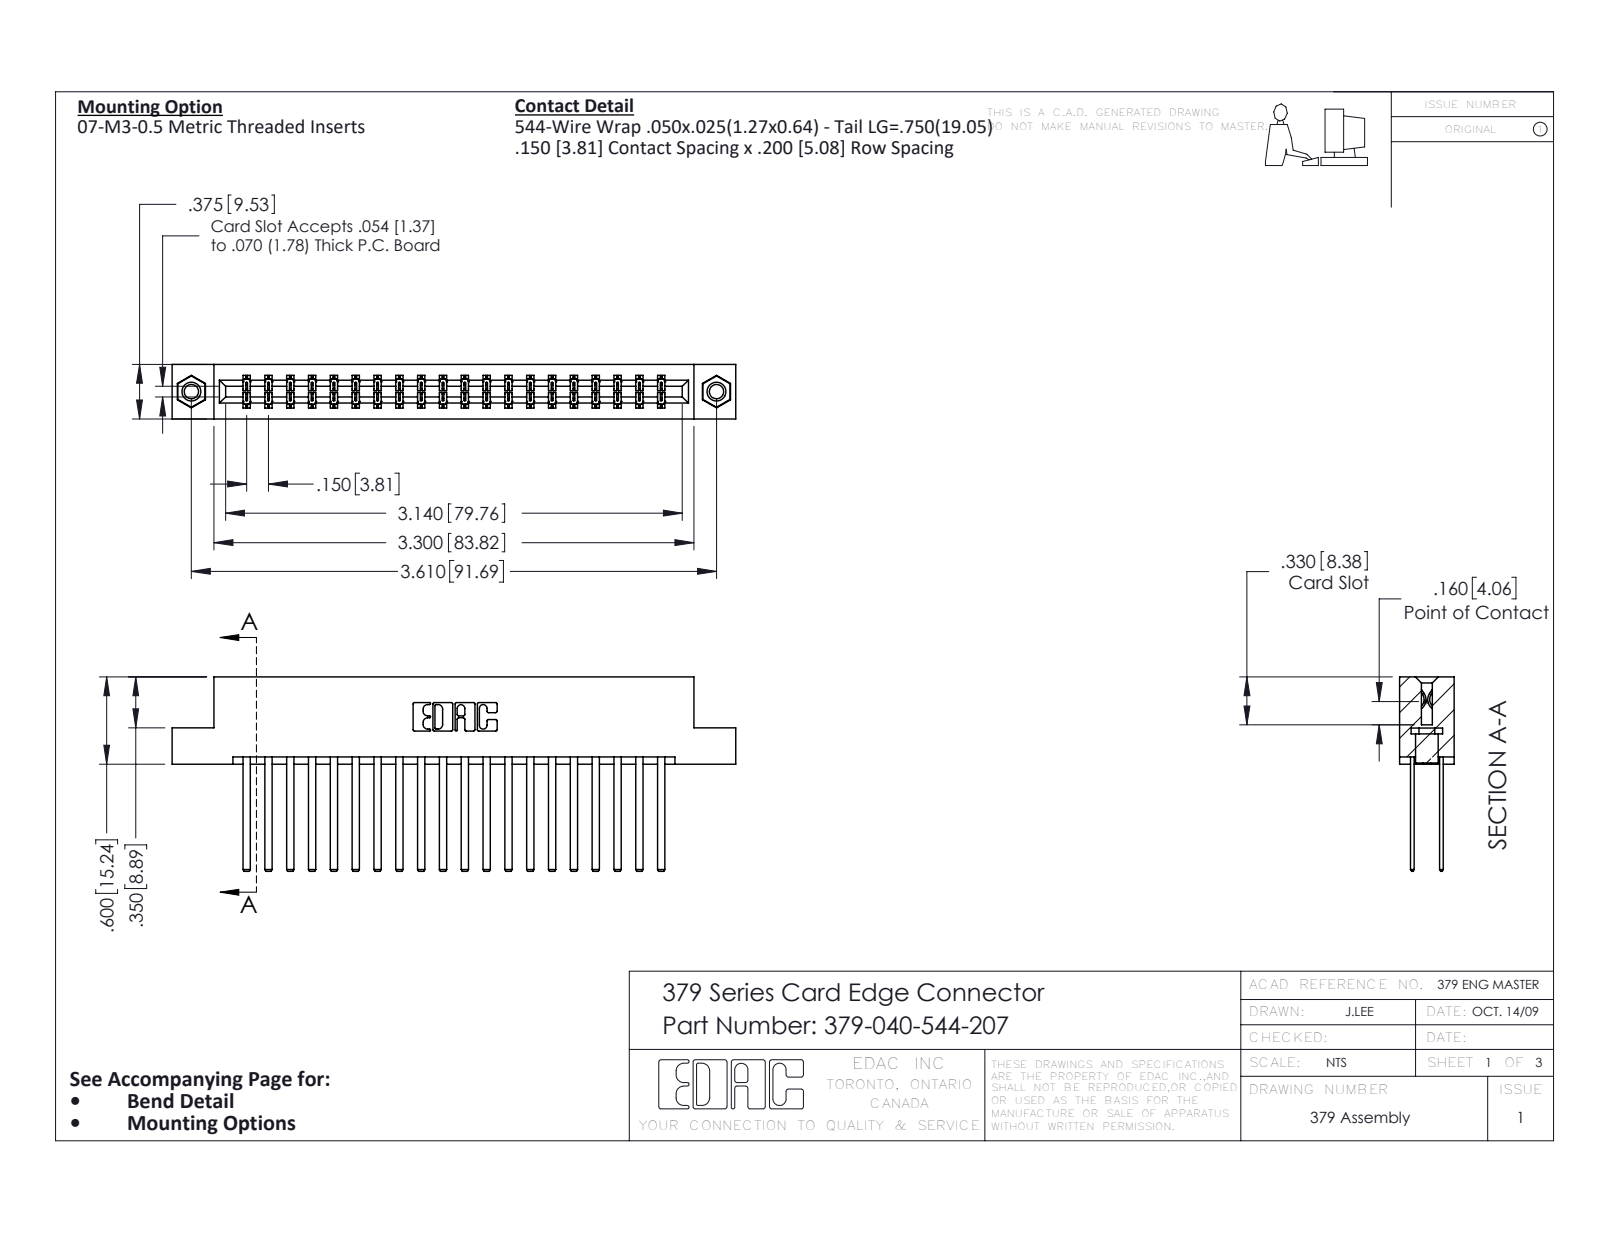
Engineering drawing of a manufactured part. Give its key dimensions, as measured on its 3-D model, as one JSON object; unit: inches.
{"part_name": "345-292-001_345-293-144; 345-250-001_345-250-005-103; 379-040-544-207; 379 Part_Flush - .156 Dia - TI", "step_written_by": "SolidWorks 2016 (CONFIG_CONTROL_DESIGN)", "units": "inches", "bodies": {"solids": 43, "faces": 2014, "planar": 1382, "cylindrical": 616, "other": 16}, "overall_size": [3.875, 1.337, 0.375], "volume_in3": 0.656, "surface_area_in2": 21.32, "round_holes": [[0.098, 2], [0.125, 2], [0.156, 2]], "round_bosses_or_shafts": [[0.155, 2]], "partial_cylinders_radius": [[0.006, 60], [0.01, 22], [0.007, 6], [0.031, 6], [0.026, 3], [0.014, 2], [0.022, 2], [0.024, 2]], "face_to_face_distances": [0.3, 0.075, 0.275, 0.1, 0.6, 0.2, 0.15, 0.375, 0.45, 0.025], "hole_center_spacings": [3.61]}
